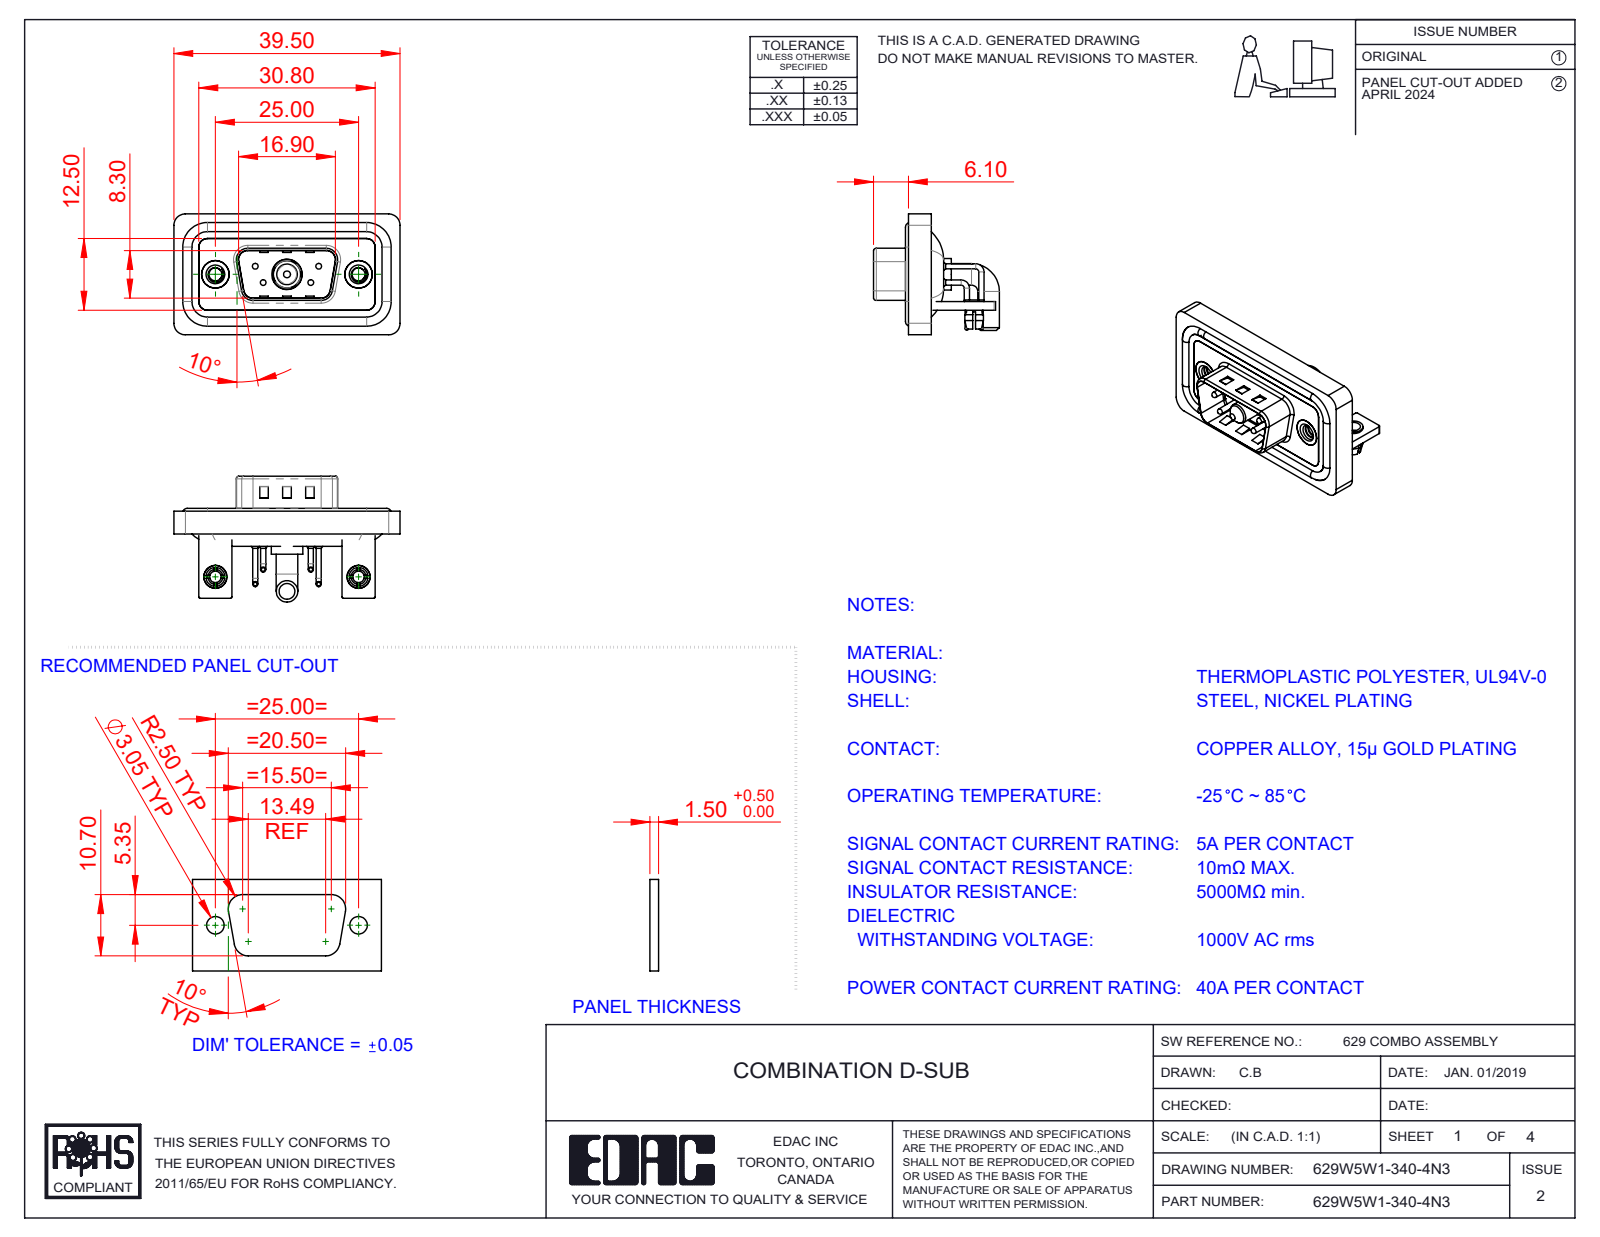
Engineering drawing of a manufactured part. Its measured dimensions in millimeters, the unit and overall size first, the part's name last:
Units: millimetres
Overall size (bounding box): 39.5 × 21.98 × 21.1
Round holes (diameter × count): ⌀2 ×6, ⌀0.75 ×4, ⌀1.6 ×4, ⌀2.26 ×2, ⌀2.5 ×2, ⌀3.2 ×2, ⌀4 ×2, ⌀4.8 ×2, ⌀5 ×2, ⌀4.85 ×1, ⌀5.3 ×1
Round bosses / shafts (diameter × count): ⌀0.9 ×8, ⌀1.6 ×4, ⌀1.5 ×4, ⌀1 ×4, ⌀0.65 ×4, ⌀4.9 ×2, ⌀4 ×2, ⌀3.75 ×2
Partial cylindrical surfaces — rounded edges, fillets, slot ends (radius × count): R2 ×19, R1.5 ×18, R0.25 ×16, R0.5 ×9, R1.6 ×8, R0.6 ×4, R0.65 ×4, R0.9 ×4
Main face-to-face distances: 0.4, 1.5, 0.8, 2.9, 1.1, 2.1, 1.2, 1.6, 2.5, 3.7
Hole centre spacings: 3.16, 5.72, 7.1, 12.5, 18.1, 25, 4.39, 4.4
Volume: 4 863 mm³ · Surface area: 8 005 mm²
Bodies: 17 solids, 1026 faces (479 planar, 395 cylindrical, 152 other)
Part name (STEP PRODUCT): Power Pin_40A RA; 629Combo Threaded Rivet_3; 629Combo Shell Front_09 Contacts; 629Combo Board Lock (+7 more)
STEP written by: SolidWorks 2023 (CONFIG_CONTROL_DESIGN)
